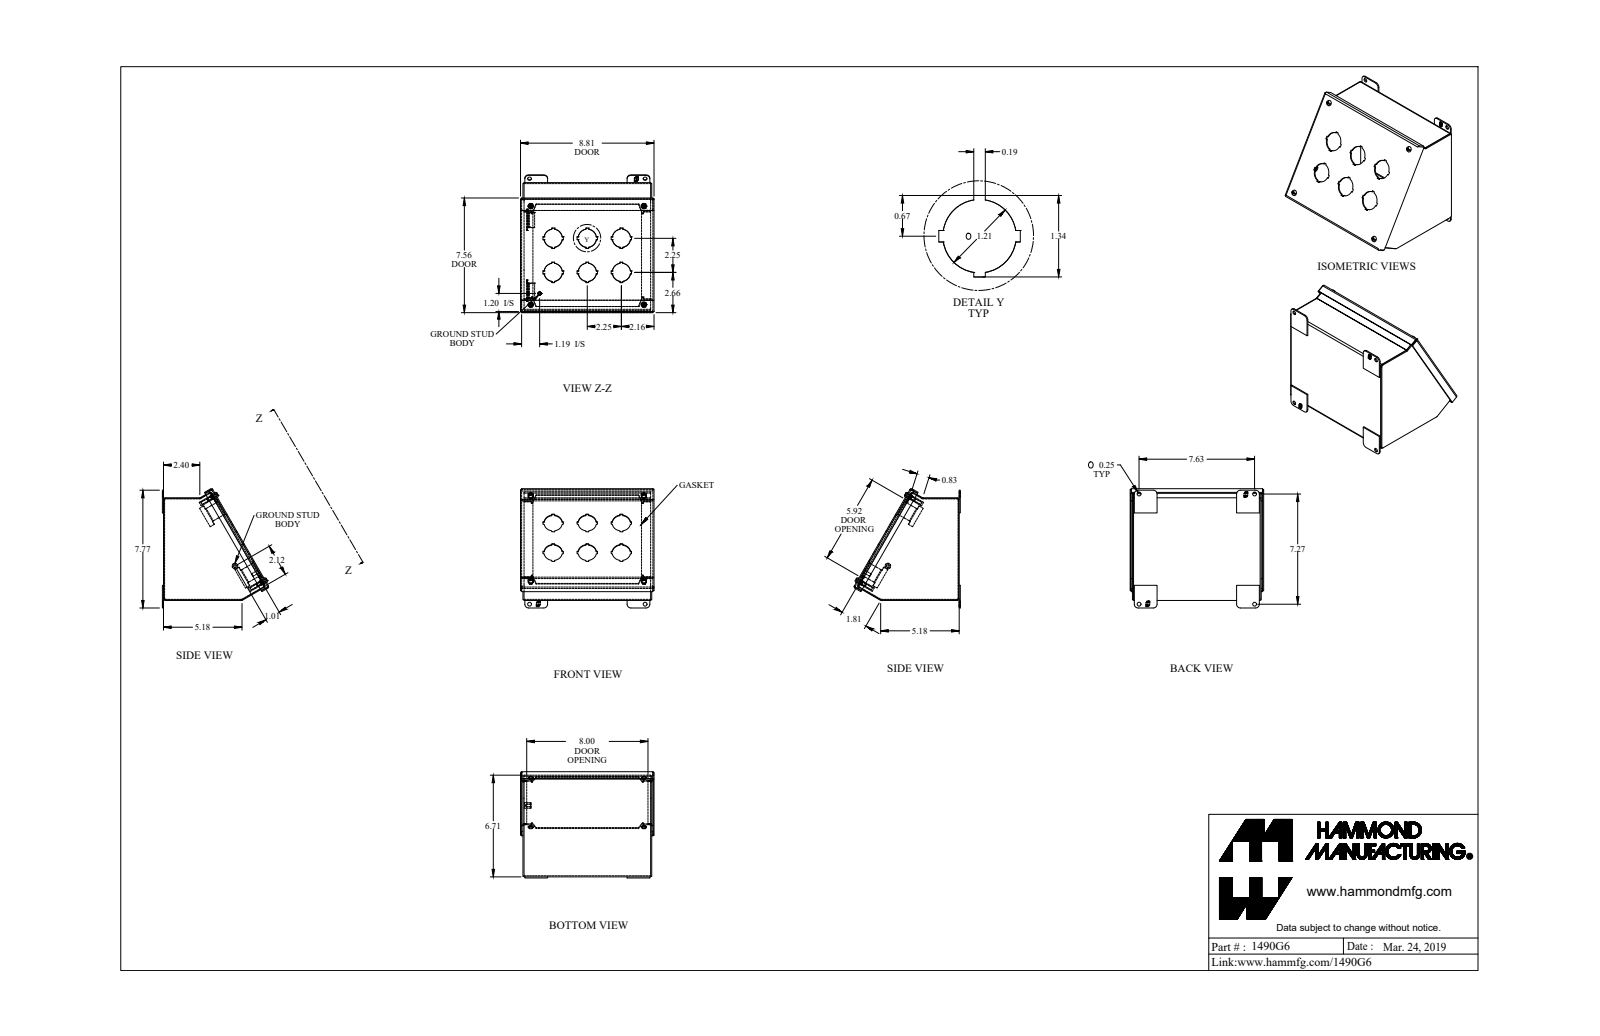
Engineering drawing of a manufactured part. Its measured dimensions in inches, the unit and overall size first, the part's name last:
Units: inches
Overall size (bounding box): 8.812 × 7.869 × 7.008
Round holes (diameter × count): ⌀0.25 ×8, ⌀1.21 ×6, ⌀0.159 ×4, ⌀0.156 ×1
Round bosses / shafts (diameter × count): ⌀0.39 ×4, ⌀0.275 ×4, ⌀0.19 ×4, ⌀0.148 ×4, ⌀0.375 ×1, ⌀0.25 ×1, ⌀0.188 ×1
Partial cylindrical surfaces — rounded edges, fillets, slot ends (radius × count): R0.108 ×18, R0.036 ×12, R0.029 ×8, R0.086 ×8, R0.25 ×8, R0.125 ×4, R0.16 ×4, R0.171 ×4
Main face-to-face distances: 0.072, 8.428, 6.697, 8.356, 8.5, 0.259, 0.187, 6.769, 6.625, 0.172
Hole centre spacings: 2.25, 6.5, 3.182, 7.409, 7.46, 7.474, 9.905, 2.589
Volume: 26.05 in³ · Surface area: 684.7 in²
Bodies: 28 solids, 805 faces (577 planar, 188 cylindrical, 40 other)
Part name (STEP PRODUCT): 1490G6_Default
STEP written by: SolidWorks 2019 (CONFIG_CONTROL_DESIGN)
